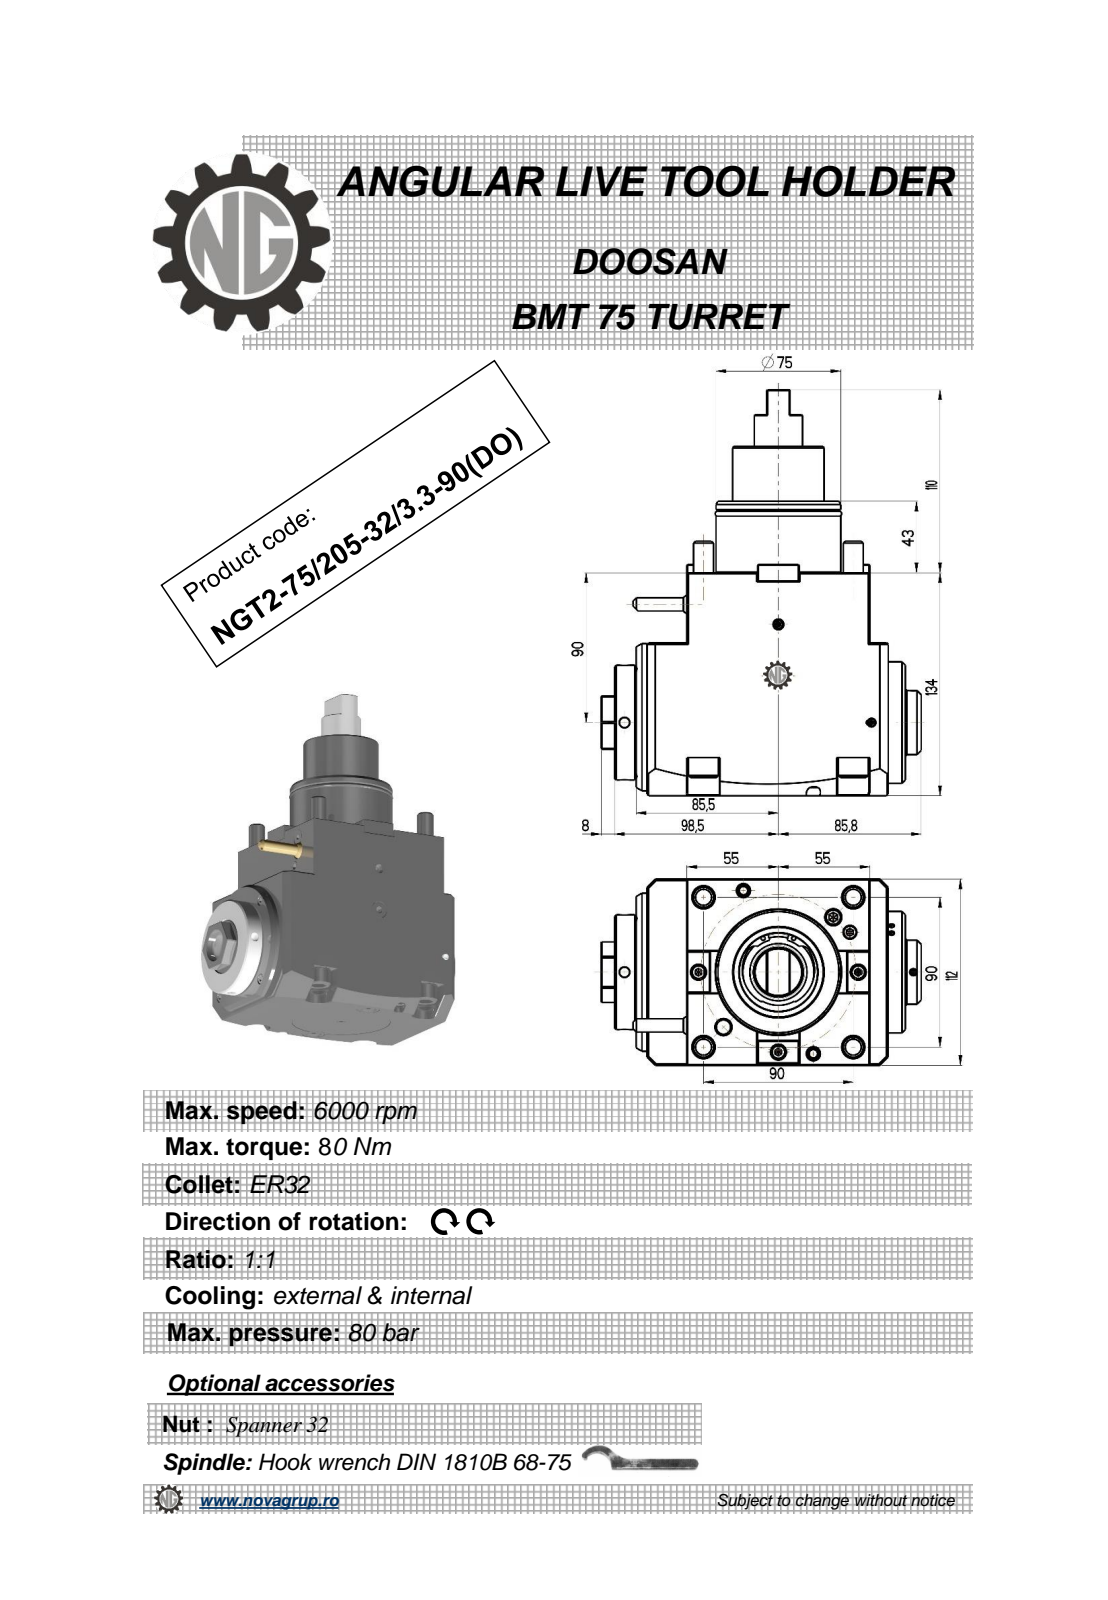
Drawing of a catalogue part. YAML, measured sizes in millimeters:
part_name: "NGT2_75_205_32_3_3_90_DO"
step_written_by: "PRO/ENGINEER BY PARAMETRIC TECHNOLOGY CORPORATION, 2010280 (CONFIG_CONTROL_DESIGN)"
units: millimeters
bodies: {solids: 2, faces: 299, planar: 147, cylindrical: 71, other: 81}
overall_size: [244, 192.3, 112]
volume: 2421000
surface_area: 139076
round_holes:
  - {diameter: 6, count: 2}
  - {diameter: 8.5, count: 2}
  - {diameter: 3, count: 1}
  - {diameter: 5, count: 1}
  - {diameter: 23, count: 1}
round_bosses_or_shafts:
  - {diameter: 18, count: 4}
  - {diameter: 12, count: 4}
  - {diameter: 95, count: 1}
  - {diameter: 75, count: 1}
  - {diameter: 74, count: 1}
  - {diameter: 73, count: 1}
  - {diameter: 70, count: 1}
  - {diameter: 69, count: 1}
partial_cylinders:
  - {radius: 9.5, count: 4}
  - {radius: 0.8, count: 2}
  - {radius: 350, count: 2}
face_to_face_distances: [112, 134, 11, 110, 121, 42, 92, 43.5, 30.5, 140.5]
hole_center_spacings: [68.04, 77.88, 93.34, 129.77]
